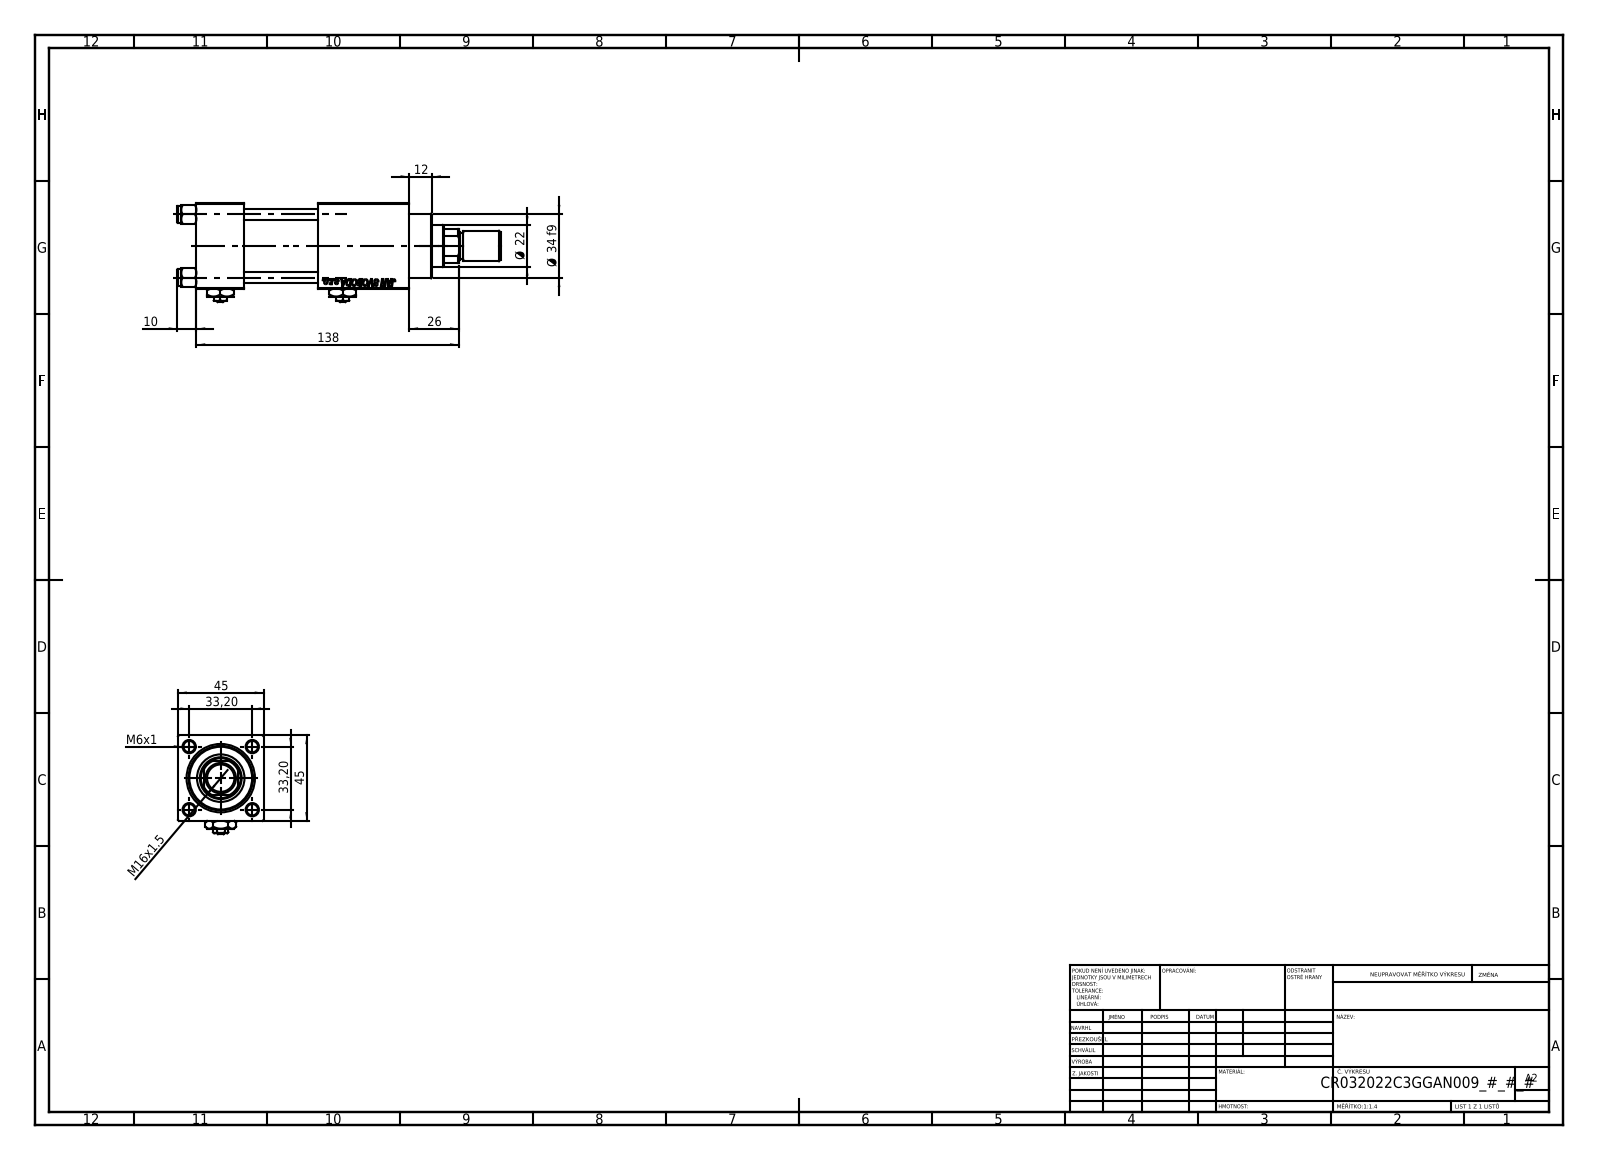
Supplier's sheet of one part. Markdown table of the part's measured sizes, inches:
| quantity | value |
| --- | --- |
| part name | V215CR_C_Body; V215_VC_A; V215CR_C_TYCINKA; Zatka_pro_OIL_PORT (+3 more) |
| STEP written by | SolidWorks 2019 (CONFIG_CONTROL_DESIGN) |
| units | inches |
| bodies | 14 solids, 1262 faces (576 planar, 102 cylindrical, 584 other) |
| overall size | 6.693 × 2.047 × 1.772 |
| volume | 12.34 in³ |
| surface area | 109.6 in² |
| round holes (diameter × count) | 0.236 × 4, 0.276 × 2, 0.518 × 2, 0.787 × 2, 0.413 × 1, 0.866 × 1, 0.945 × 1, 0.984 × 1, 1.26 × 1, 1.299 × 1 |
| round bosses / shafts (diameter × count) | 0.354 × 4, 1.496 × 1, 1.339 × 1, 0.63 × 1, 0.551 × 1 |
| partial cylindrical surfaces (radius × count) | 0.413 × 1 |
| main face-to-face distances | 1.772, 0.984, 2.52, 1.535, 1.89, 3.425, 1.764, 4.409, 2.362, 3.28 |
| hole center spacings | 0.924, 1.307, 1.848, 2.539 |
